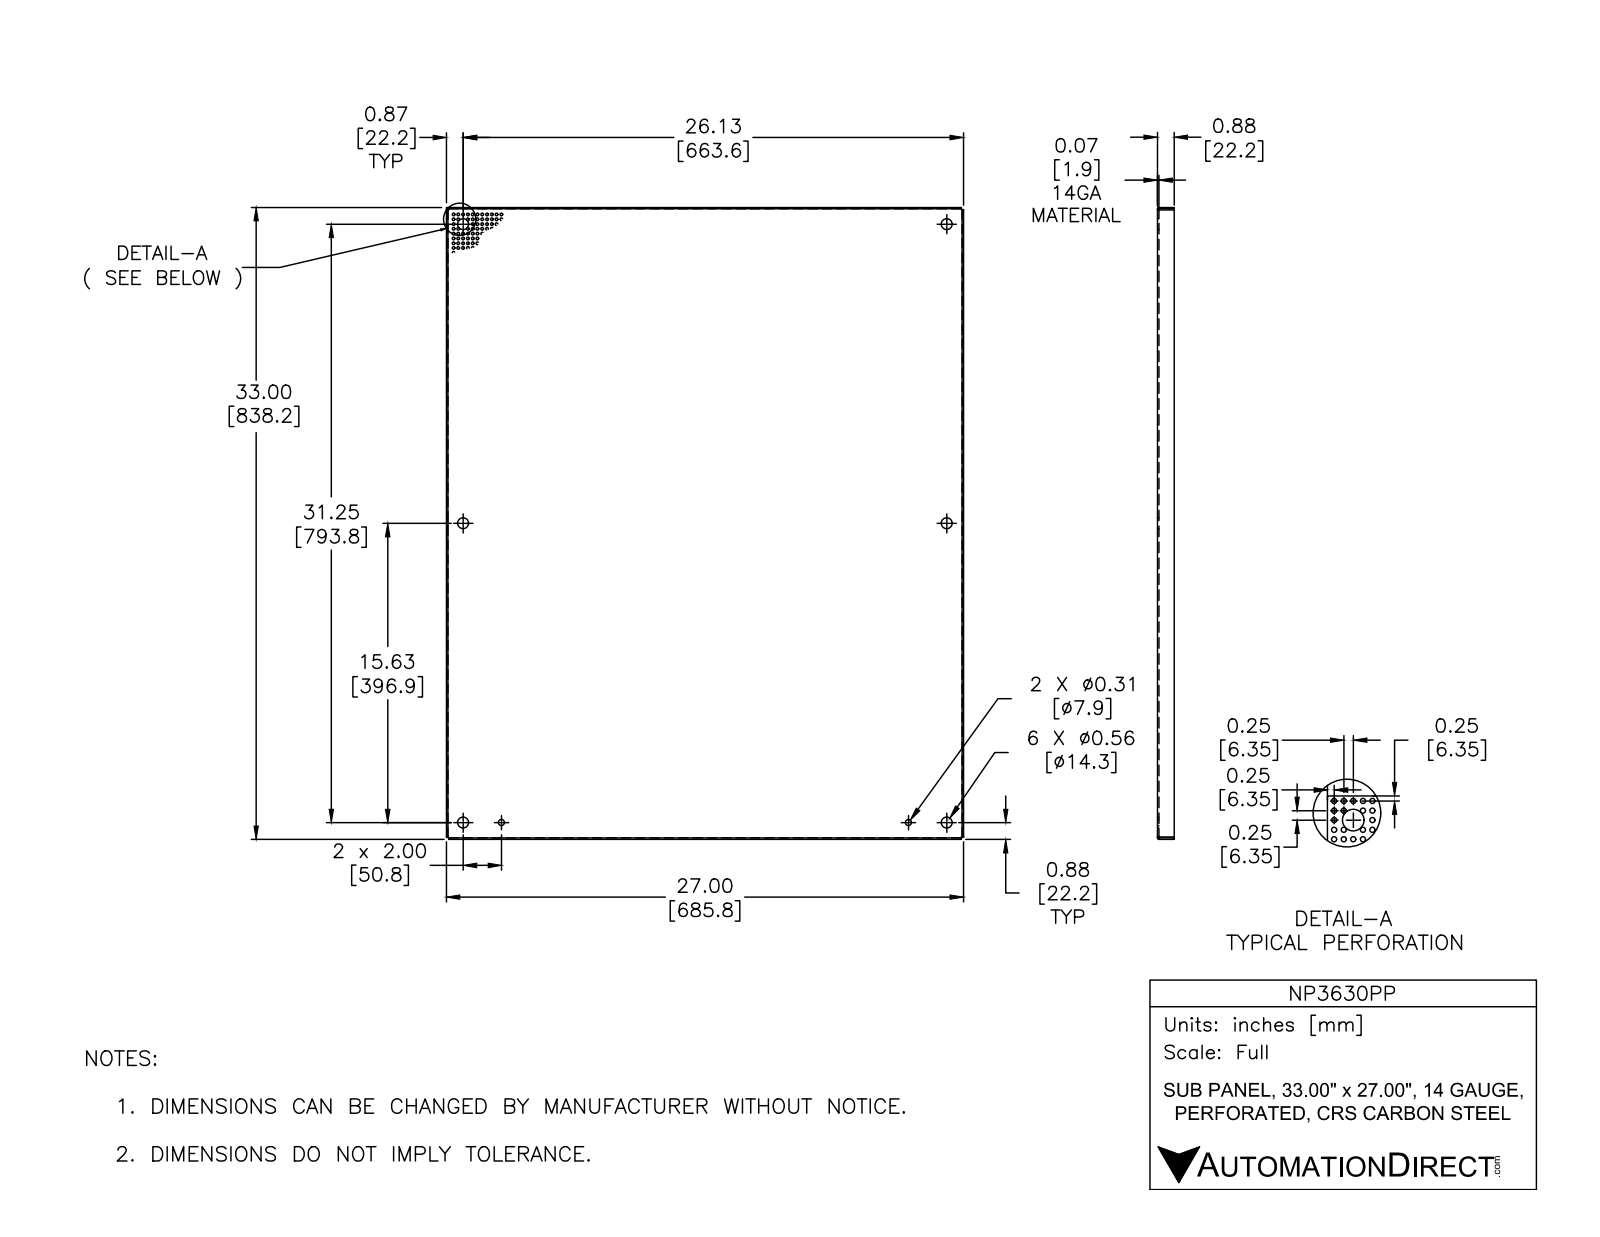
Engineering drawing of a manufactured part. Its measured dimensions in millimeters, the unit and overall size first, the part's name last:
Units: millimetres
Overall size (bounding box): 838.2 × 685.8 × 22.2
Round holes (diameter × count): ⌀14.3 ×6, ⌀7.9 ×2
Partial cylindrical surfaces — rounded edges, fillets, slot ends (radius × count): R0.8 ×4, R2.7 ×4
Main face-to-face distances: 1.9, 683.9, 836.3, 685.8, 682, 838.2, 834.4, 20.3, 22.2, 3.2
Hole centre spacings: 396.9, 396.9, 400.1, 641.4, 711.5, 754.2, 793.8, 795.4
Volume: 1 190 000 mm³ · Surface area: 1 273 000 mm²
Bodies: 1 solid, 46 faces (22 planar, 16 cylindrical, 8 other)
Part name (STEP PRODUCT): NP3630PP
STEP written by: Autodesk Inventor 2012 (AUTOMOTIVE_DESIGN)
